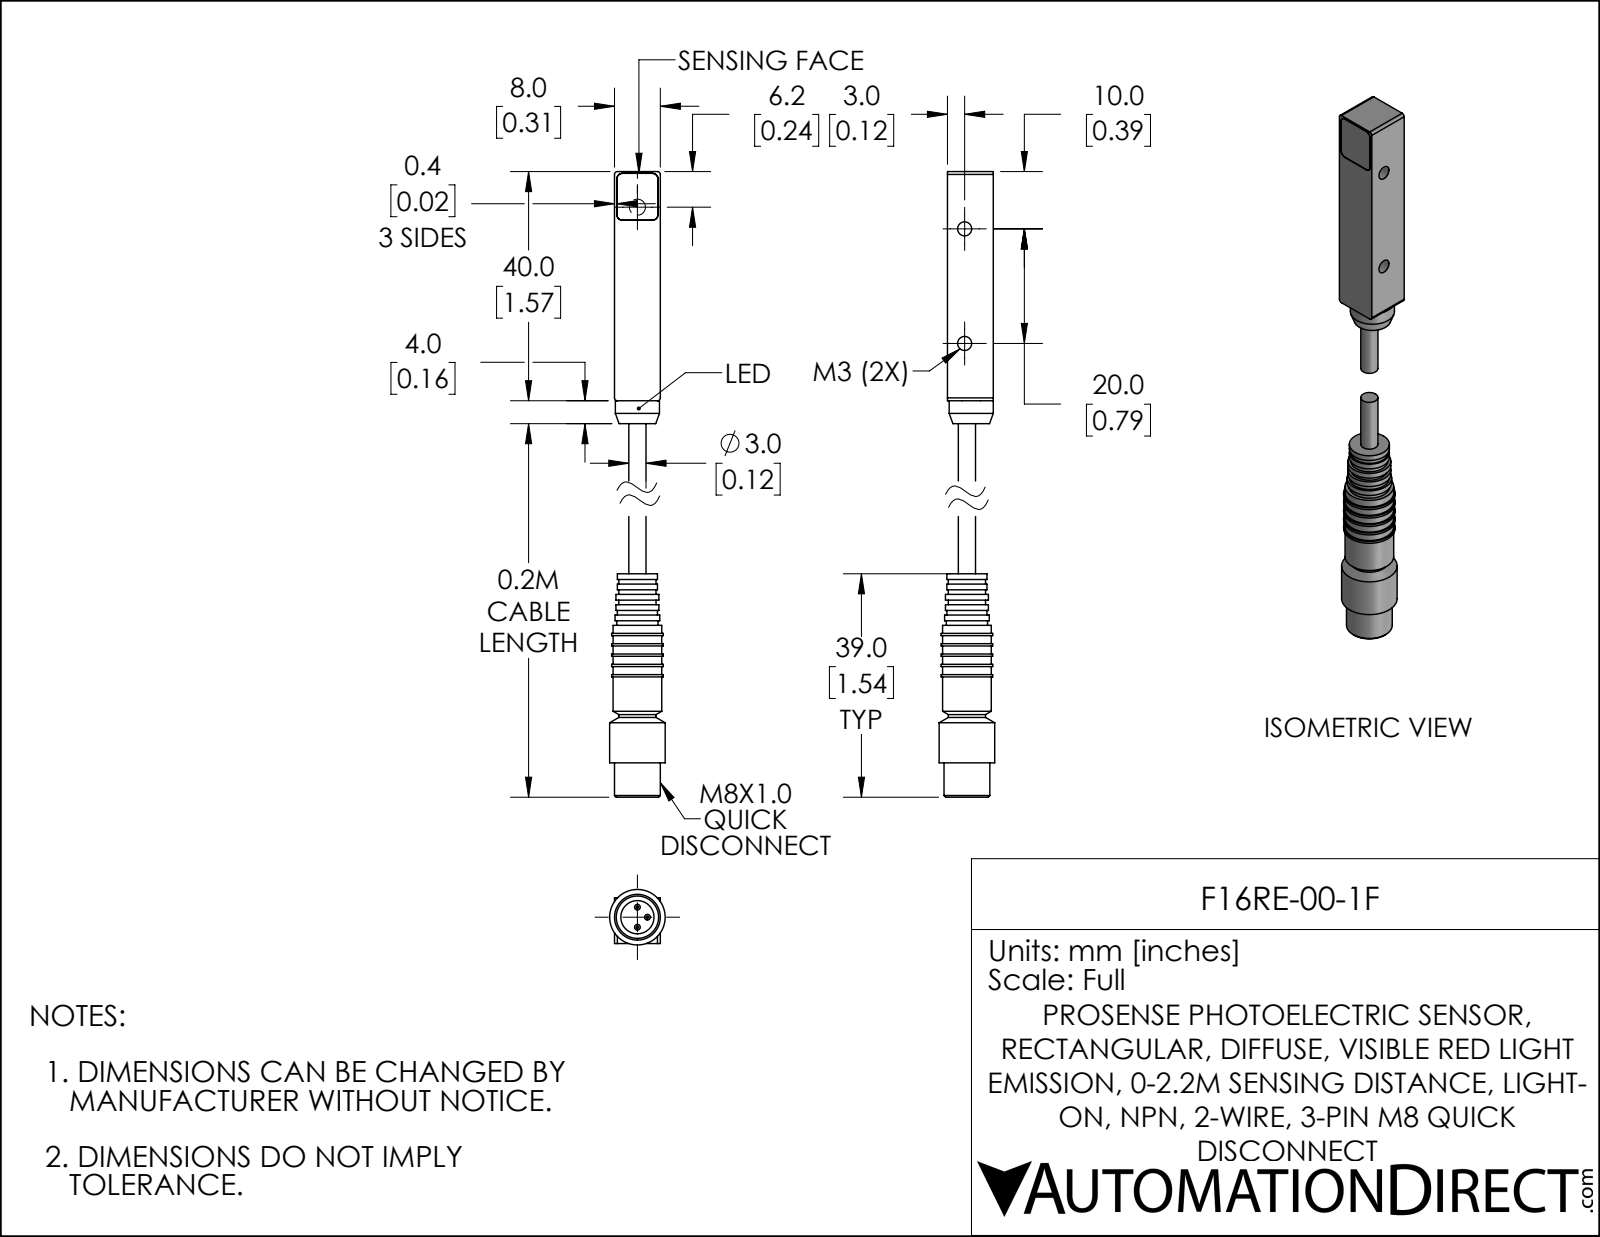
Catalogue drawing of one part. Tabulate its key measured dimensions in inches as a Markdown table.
| quantity | value |
| --- | --- |
| part name | F16RE-00-1F; F16RE-00-1F_1; F16RE-00-1F_2 |
| STEP written by | SolidWorks 2019 (AUTOMOTIVE_DESIGN) |
| units | inches |
| bodies | 2 solids, 102 faces (50 planar, 45 cylindrical, 7 other) |
| overall size | 4.327 × 0.382 × 0.382 |
| volume | 0.293 in³ |
| surface area | 5.017 in² |
| round holes (diameter × count) | 0.097 × 2, 0.228 × 1 |
| round bosses / shafts (diameter × count) | 0.039 × 3, 0.382 × 1, 0.354 × 1, 0.335 × 1, 0.315 × 1, 0.307 × 1, 0.303 × 1, 0.295 × 1 |
| partial cylindrical surfaces (radius × count) | 0.02 × 4, 0.039 × 4, 0.039 × 4 |
| main face-to-face distances | 0.315, 0.071, 0.142, 0.039, 0.354, 1.732, 2.792, 2.398, 0.213, 1.059 |
| hole center spacings | 0.787 |
